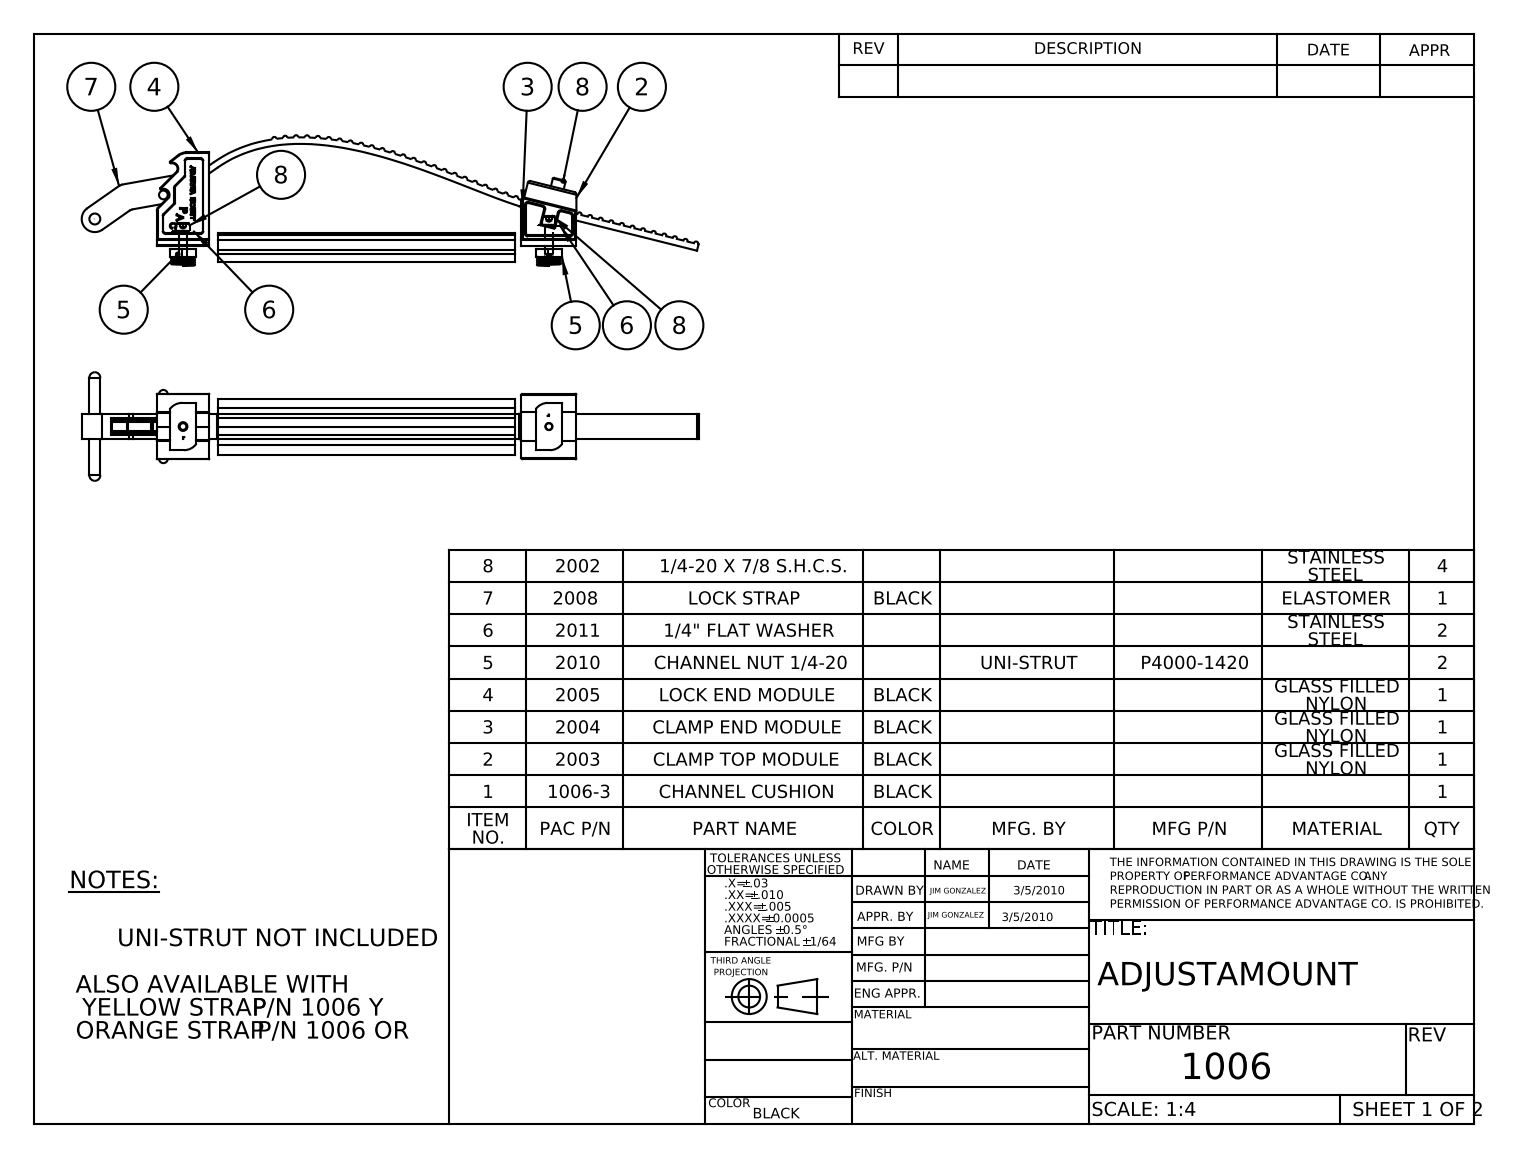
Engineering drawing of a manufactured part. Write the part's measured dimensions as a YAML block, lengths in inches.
part_name: "2004; 2011; 2008 - IN USE; 1006 (+5 more)"
step_written_by: "SolidWorks 2014 (CONFIG_CONTROL_DESIGN)"
units: inches
bodies: {solids: 16, faces: 1002, planar: 402, cylindrical: 334, other: 266}
overall_size: [17.642, 3.741, 3.106]
volume: 16.69
surface_area: 172.4
round_holes:
  - {diameter: 0.201, count: 4}
  - {diameter: 0.25, count: 2}
  - {diameter: 0.288, count: 2}
  - {diameter: 0.26, count: 1}
  - {diameter: 0.291, count: 1}
  - {diameter: 0.625, count: 1}
  - {diameter: 0.64, count: 1}
round_bosses_or_shafts:
  - {diameter: 0.25, count: 5}
  - {diameter: 0.375, count: 4}
  - {diameter: 0.625, count: 1}
  - {diameter: 0.313, count: 1}
partial_cylinders:
  - {radius: 0.062, count: 68}
  - {radius: 0.063, count: 52}
  - {radius: 0.031, count: 35}
  - {radius: 0.02, count: 30}
  - {radius: 0.06, count: 8}
  - {radius: 0.25, count: 4}
  - {radius: 0.424, count: 4}
  - {radius: 0.156, count: 2}
face_to_face_distances: [0.188, 0.187, 0.5, 0.73, 0.437, 0.25, 0.029, 0.759, 0.543, 0.572]
hole_center_spacings: [1.375, 10.464]
